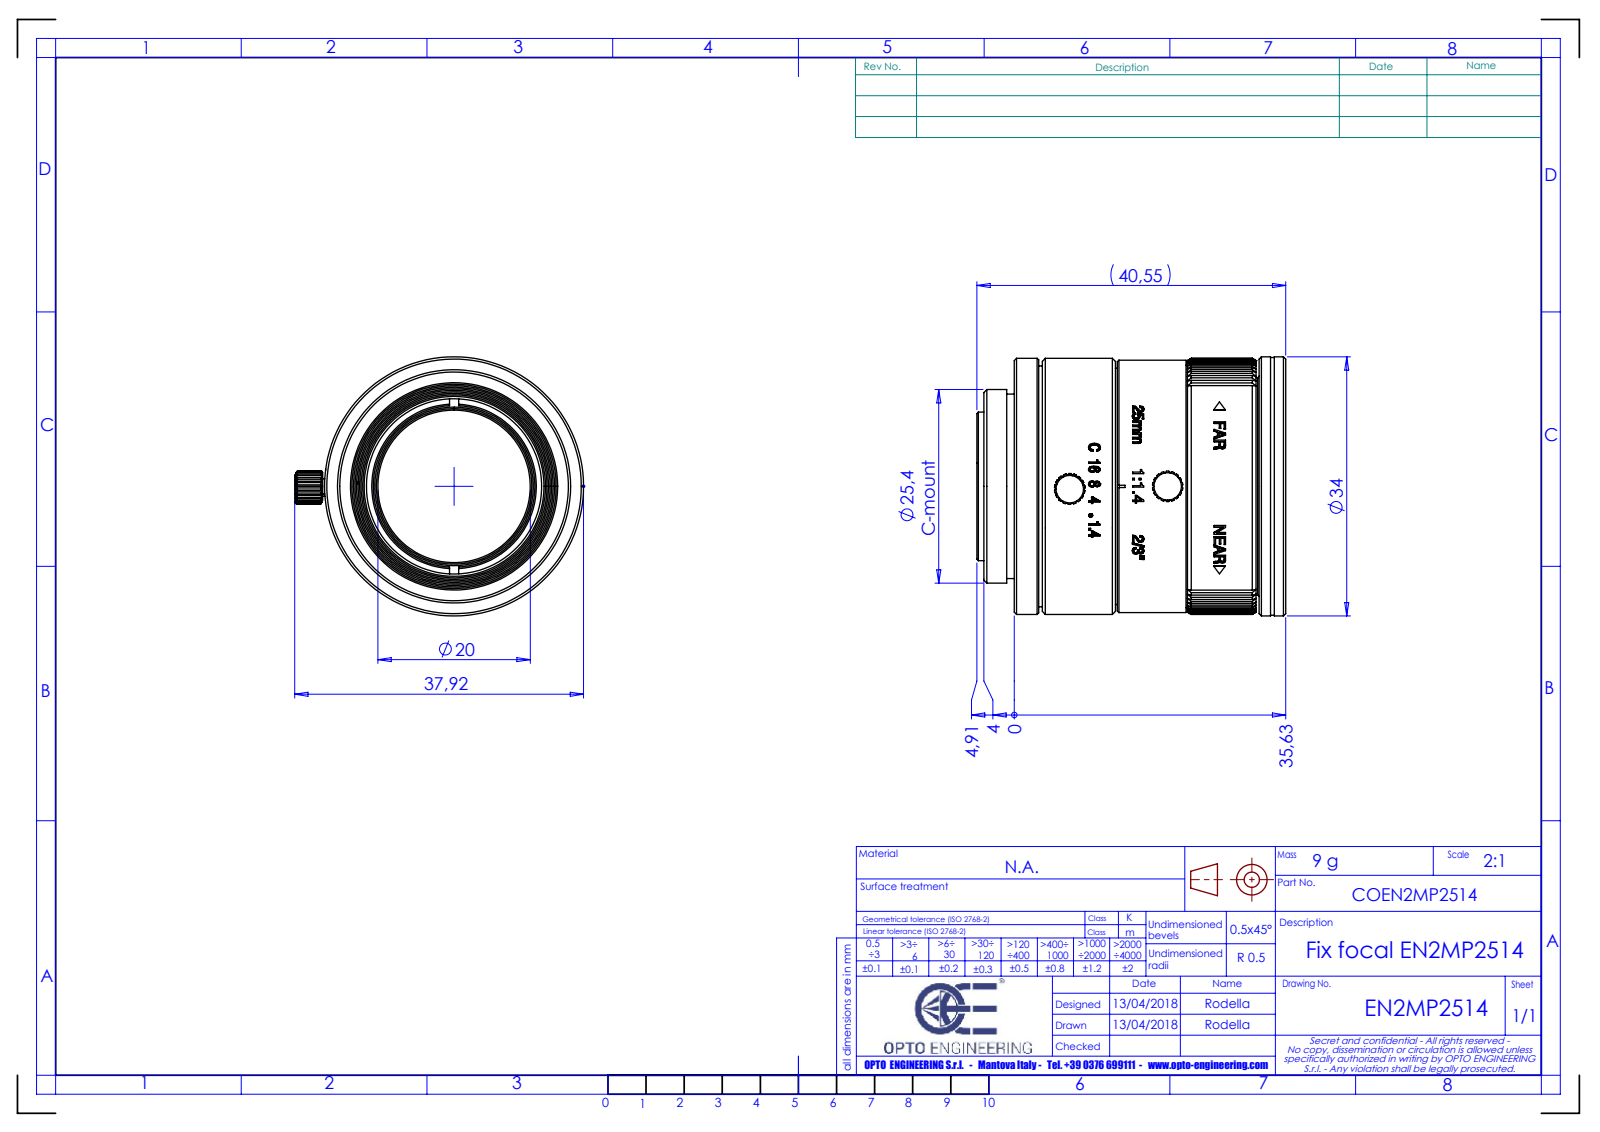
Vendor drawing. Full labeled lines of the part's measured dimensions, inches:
Part name (STEP PRODUCT): M1425MP-A-016-1_4_AF0; M1425MP-A-017_2_AF0; M1425MP-A-001_2_AF0; PRT0033 (+8 more)
STEP written by: PRO/ENGINEER BY PARAMETRIC TECHNOLOGY CORPORATION, 2011310 (AUTOMOTIVE_DESIGN)
Units: inches
Bodies: 17 solids, 1513 faces (724 planar, 332 cylindrical, 457 other)
Overall size (bounding box): 1.596 × 1.493 × 1.339
Volume: 0.572 in³ · Surface area: 26.21 in²
Round holes (diameter × count): ⌀0.079 ×4, ⌀0.063 ×3, ⌀0.071 ×3, ⌀0.551 ×1, ⌀0.638 ×1, ⌀0.685 ×1, ⌀0.787 ×1, ⌀0.803 ×1, ⌀0.819 ×1, ⌀0.827 ×1, ⌀0.835 ×1, ⌀0.85 ×1
Round bosses / shafts (diameter × count): ⌀0.079 ×2, ⌀1.339 ×1, ⌀1.331 ×1, ⌀1.323 ×1, ⌀1.303 ×1, ⌀1.244 ×1, ⌀1.122 ×1, ⌀1.063 ×1
Partial cylindrical surfaces — rounded edges, fillets, slot ends (radius × count): R0.079 ×2, R0.03 ×1, R0.648 ×1, R0.654 ×1, R0.655 ×1, R0.656 ×1
Main face-to-face distances: 0.022, 0.016, 0.039, 0.847, 0.869, 0.396, 1.243, 1.265, 0.38, 1.228
Hole centre spacings: 0.551, 0.955, 0.954
